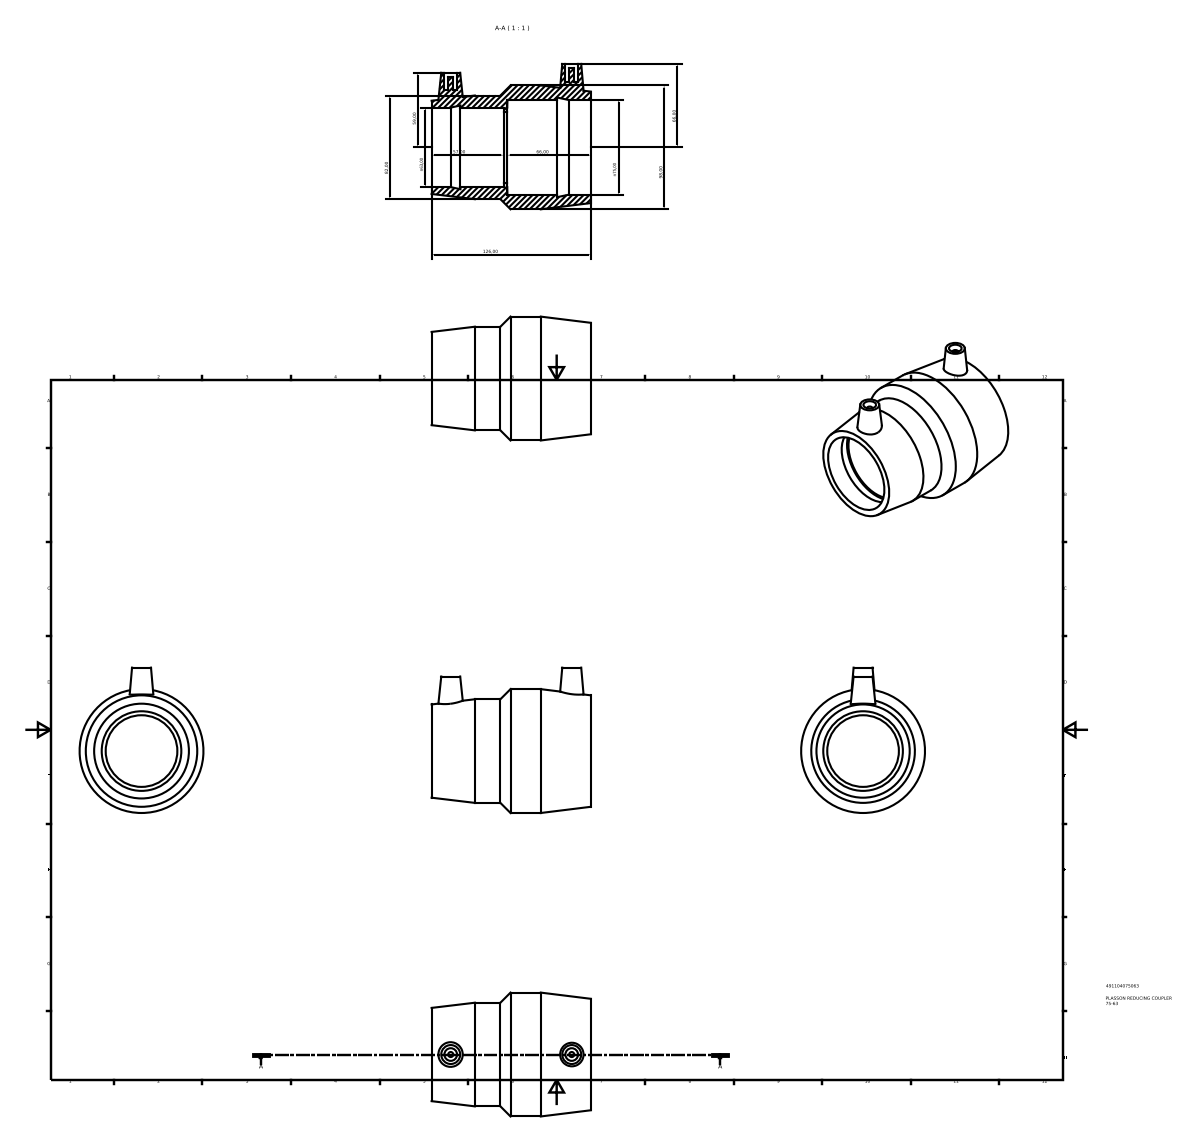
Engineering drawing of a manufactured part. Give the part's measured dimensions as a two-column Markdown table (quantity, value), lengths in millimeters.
| quantity | value |
| --- | --- |
| part name | 491104075063 |
| STEP written by | Autodesk Inventor 2015 (AUTOMOTIVE_DESIGN) |
| units | millimeters |
| bodies | 1 solid, 31 faces (12 planar, 11 cylindrical, 8 other) |
| overall size | 126 × 115 × 98 |
| volume | 298 800 mm³ |
| surface area | 72 678 mm² |
| round holes (diameter × count) | 10 × 2, 56.7 × 1, 63 × 1, 75 × 1 |
| round bosses / shafts (diameter × count) | 4 × 2, 98 × 1, 82 × 1 |
| main face-to-face distances | 126, 59.85, 66.15, 57, 2.85, 69, 99.6, 42.6, 39.75, 26.4 |
| hole center spacings | 95.76 |
